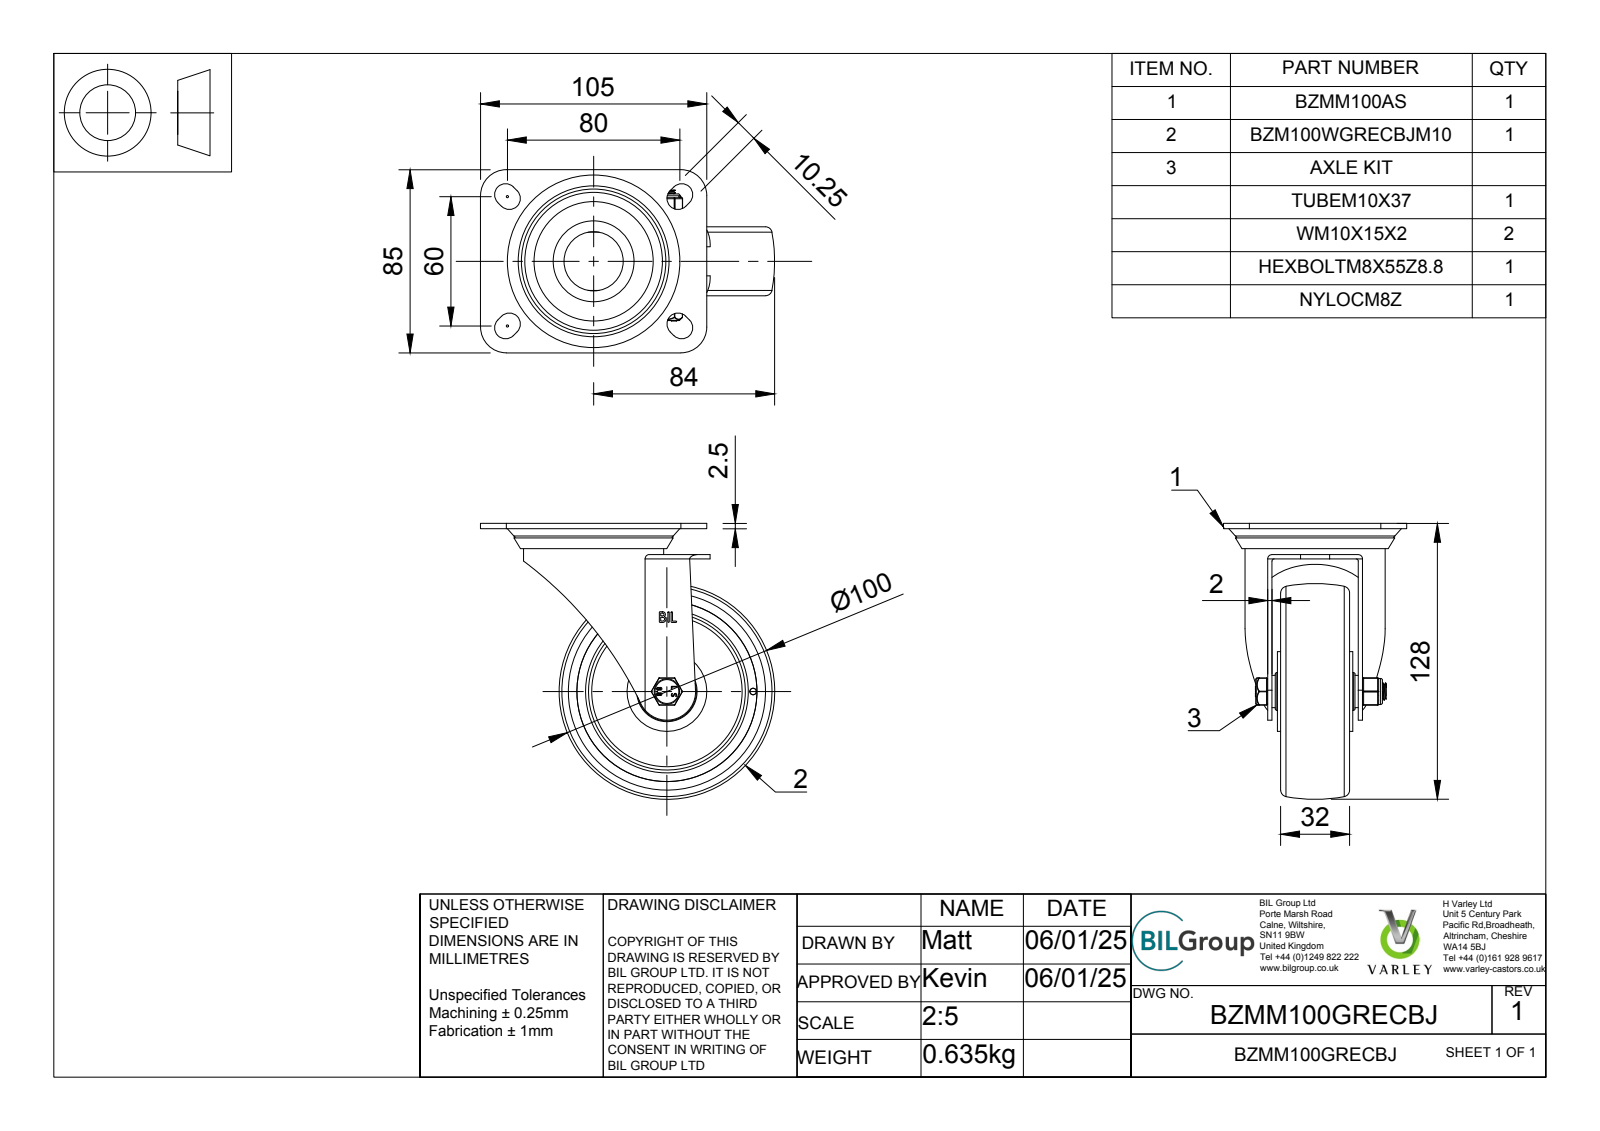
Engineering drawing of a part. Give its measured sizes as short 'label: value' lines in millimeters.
name: BZMM100GRECBJ v3; BZMM100AS - 2 v2; ZINC PLATED, PRESSED STEEL TOP PLATE; ZINC PLATED, PRESSED STEEL TOP PLATE Geometry (+7 more)
written by: Autodesk Translation Framework v13.20.0.188 (AP242_MANAGED_MODEL_BASED_3D_ENGINEERING_MIM_LF)
unit: mm
bodies: 54 solids, 451 faces (142 planar, 155 cylindrical, 154 other)
size: 136.5 × 128 × 85
volume: 213 151 mm³; area: 116 879 mm²
holes: 2× ⌀0.66, 1× ⌀3, 1× ⌀8, 1× ⌀8.2, 1× ⌀8.25, 1× ⌀8.6, 1× ⌀10.1, 1× ⌀10.25, 1× ⌀18, 1× ⌀18.6, 1× ⌀25.5, 1× ⌀27.5
bosses: 1× ⌀65, 1× ⌀37, 1× ⌀31.5, 1× ⌀17.5, 1× ⌀15, 1× ⌀12.1, 1× ⌀11.5, 1× ⌀10
rounds: 18× R0.5, 12× R0.25, 8× R5.12, 4× R0.33, 4× R0.64, 4× R1, 4× R12, 2× R0.63
face distances: 2, 2.5, 13.5, 18.5, 22.5, 36, 4, 6, 19.5, 24.5
hole spacings: 3.22, 42.99, 2.49, 40
